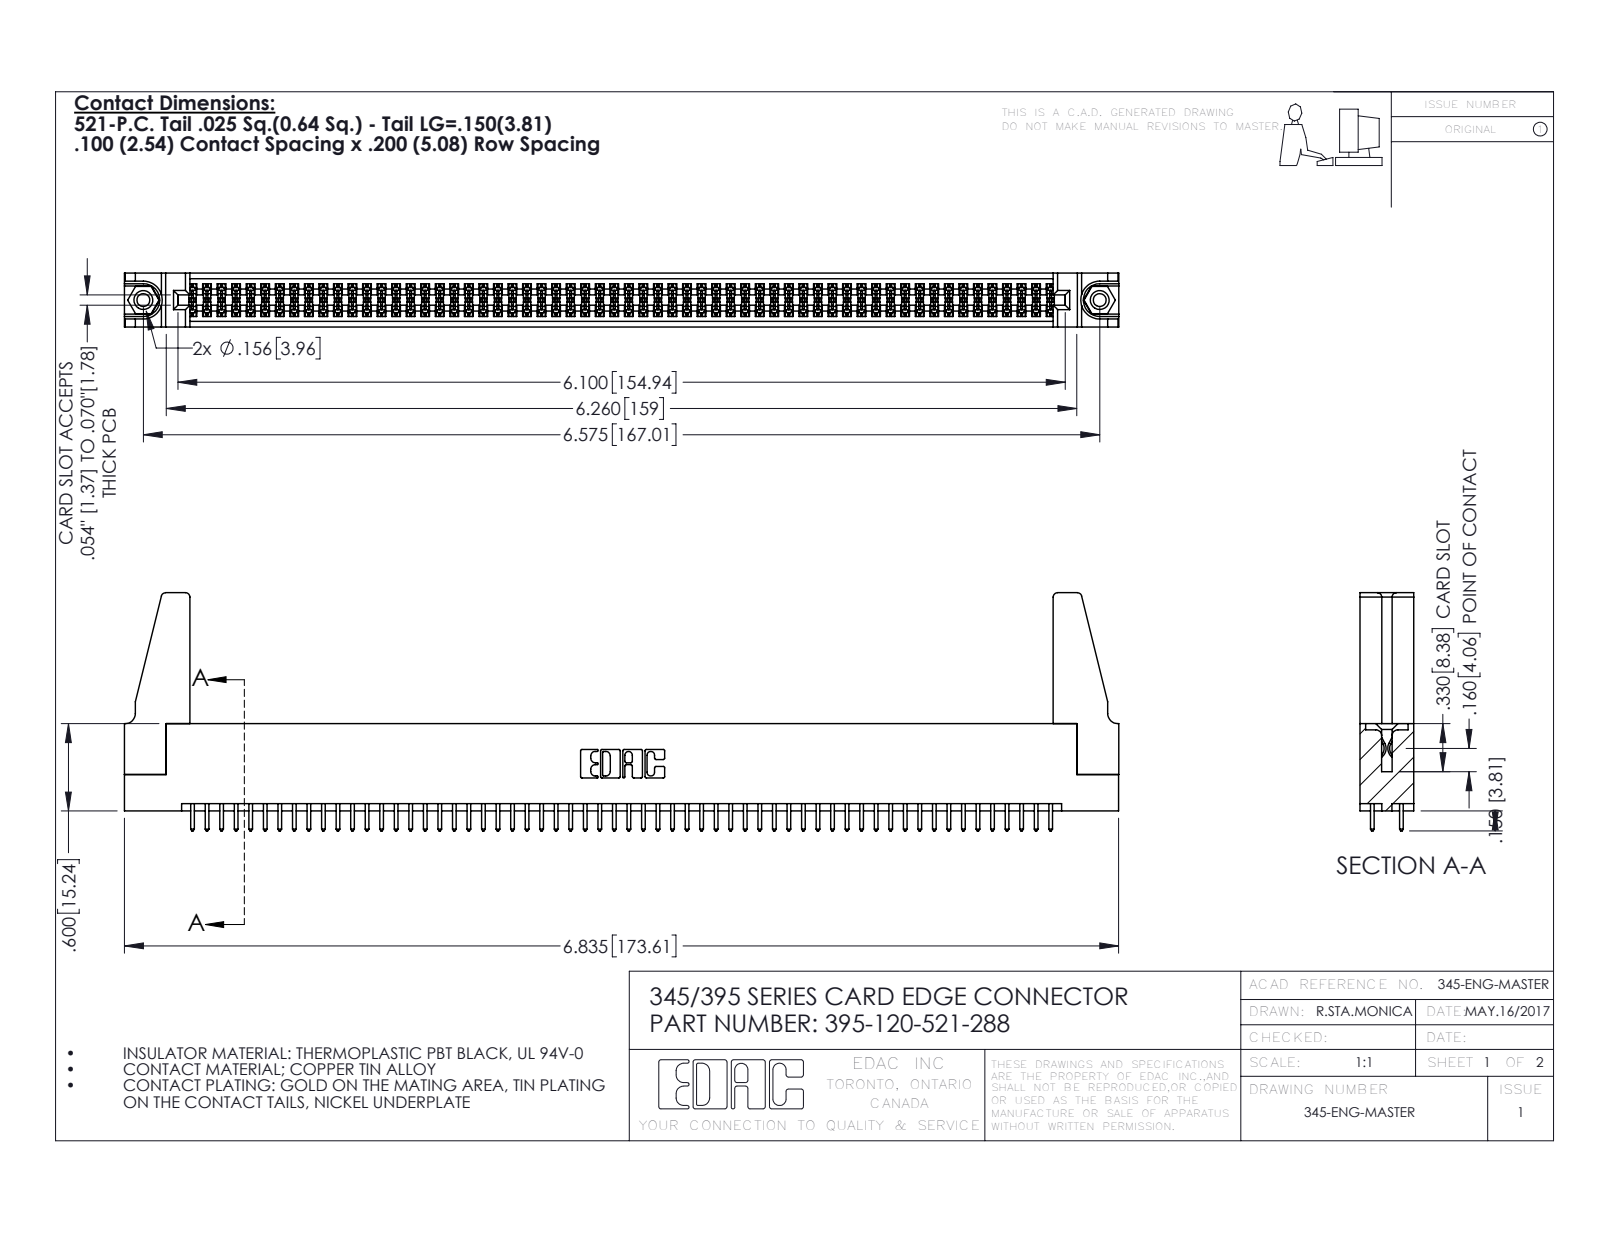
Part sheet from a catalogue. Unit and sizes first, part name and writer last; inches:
Units: inches
Overall size (bounding box): 6.836 × 1.637 × 0.37
Round holes (diameter × count): ⌀0.089 ×2, ⌀0.125 ×2, ⌀0.156 ×2, ⌀0.064 ×1
Round bosses / shafts (diameter × count): ⌀0.155 ×2
Partial cylindrical surfaces — rounded edges, fillets, slot ends (radius × count): R0.006 ×180, R0.01 ×120, R0.01 ×22, R0.03 ×8, R0.007 ×6, R0.031 ×6, R0.026 ×3, R0.014 ×2
Main face-to-face distances: 0.072, 0.298, 0.37, 0.2, 0.098, 0.272, 0.025, 0.225, 0.175, 0.149
Hole centre spacings: 0.27, 6.339, 6.575
Volume: 1.235 in³ · Surface area: 43.8 in²
Bodies: 125 solids, 6250 faces (4112 planar, 2122 cylindrical, 16 other)
Part name (STEP PRODUCT): 345-250-001_345-250-001-102; 345-292-001_345-293-121; 345 Part_Flush Mounting Lugs - 0.156 Dia-TH; 345-220-078_345-220-088 (+1 more)
STEP written by: SolidWorks 2016 (CONFIG_CONTROL_DESIGN)
